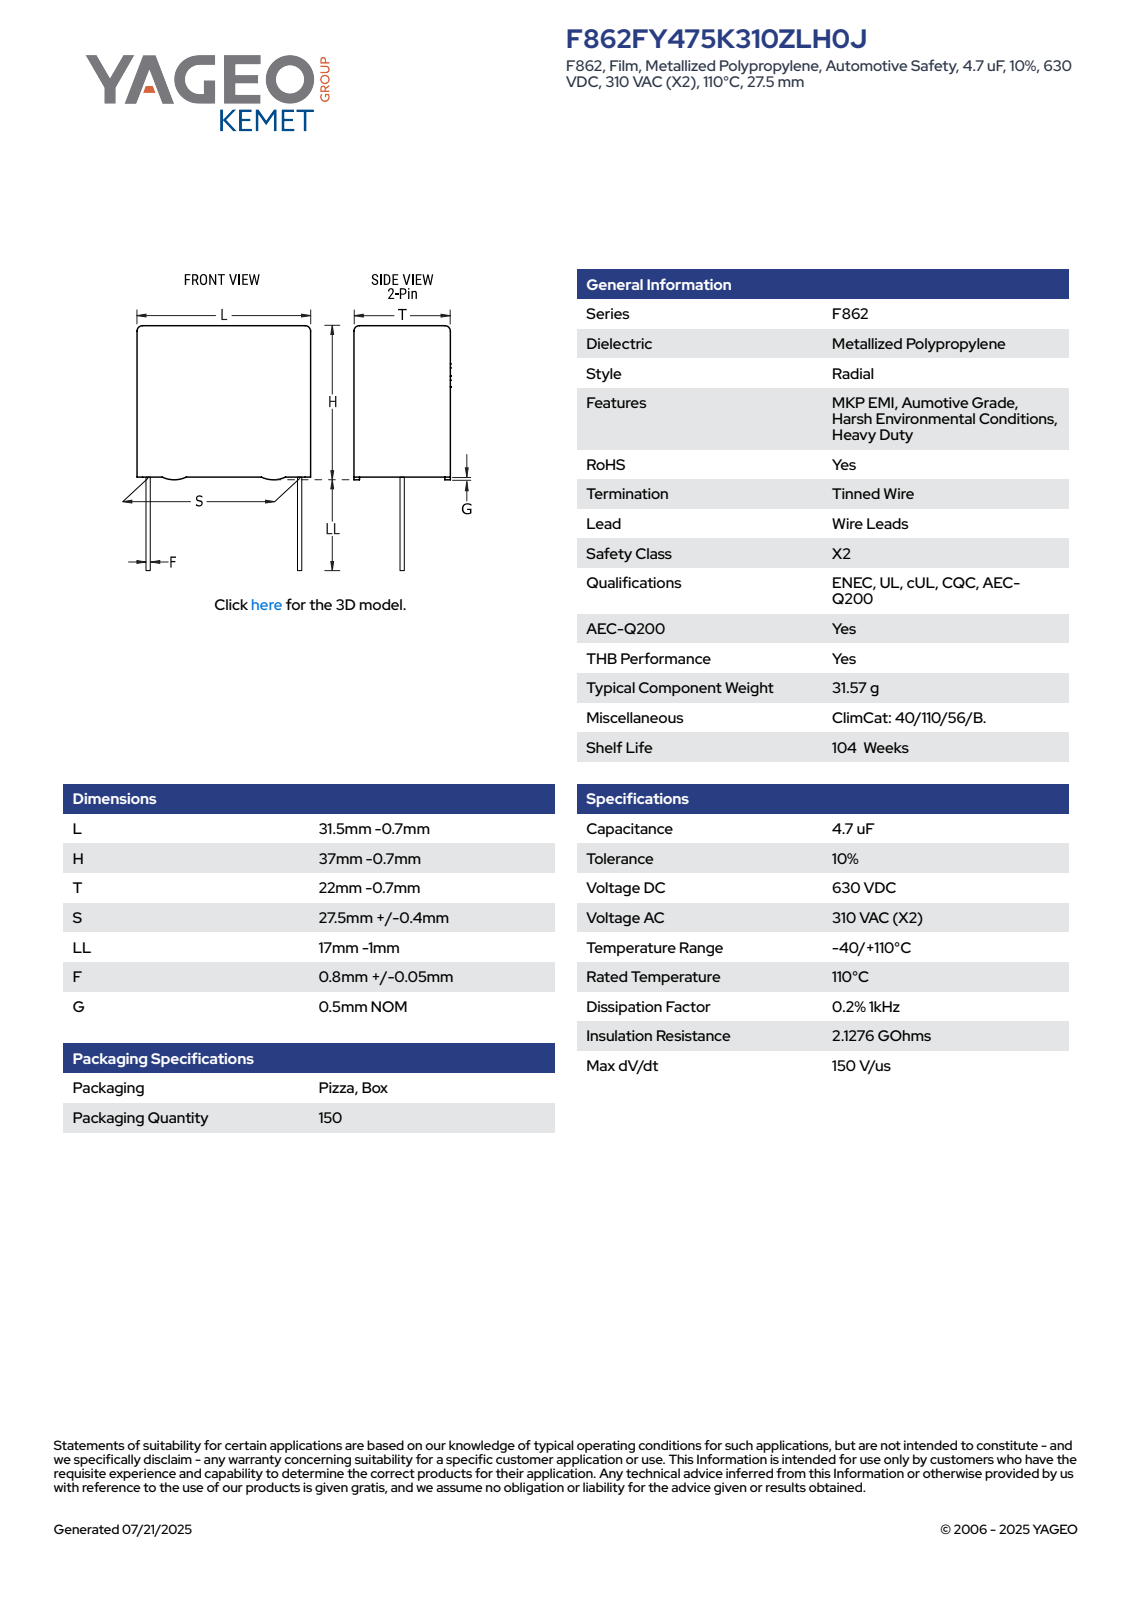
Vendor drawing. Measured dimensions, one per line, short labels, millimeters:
name: CFR_RBG_31.5X37X22_L30.8H36.3T21.3S27.5LL16F0.85G0.5
written by: SolidWorks 2014 (AUTOMOTIVE_DESIGN)
unit: mm
bodies: 4 solids, 89 faces (81 planar, 8 cylindrical, 0 other)
size: 52.3 × 30.8 × 21.3
volume: 23 511 mm³; area: 5 233 mm²
bosses: 2× ⌀0.85
rounds: 4× R0.5
face distances: 21.3, 30.8, 35.8, 0.5, 36.3, 1.21, 20.09, 18.88, 16.82, 16.83
